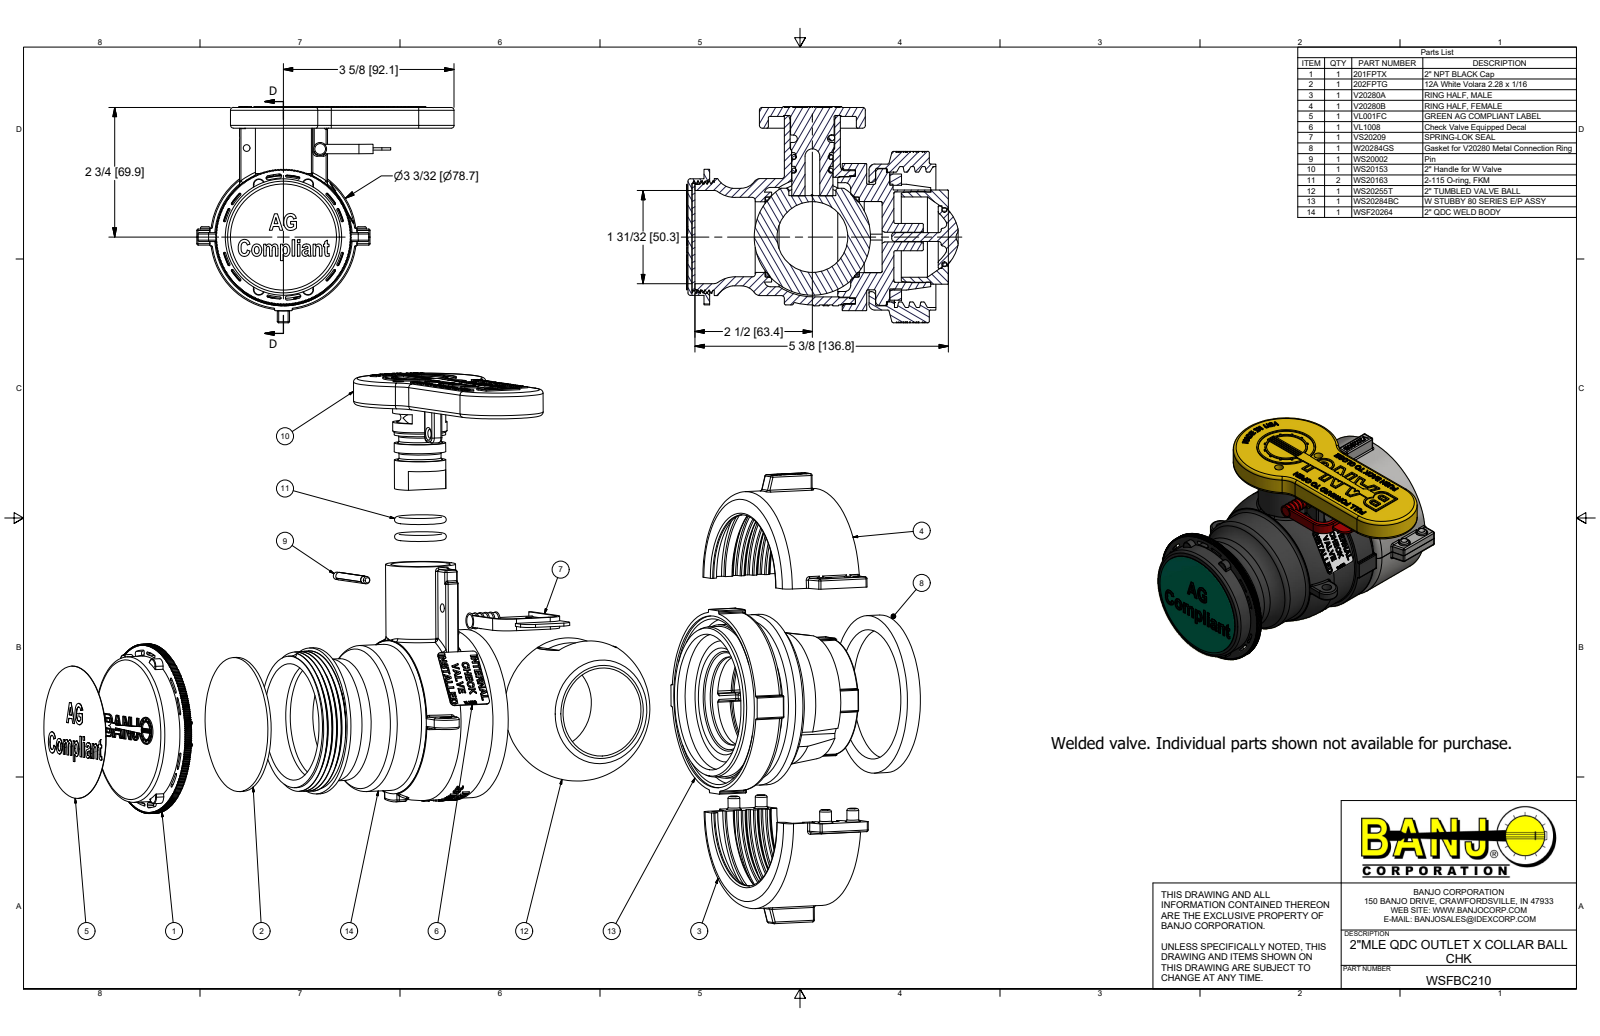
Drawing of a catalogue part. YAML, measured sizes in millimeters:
part_name: "WSF20264X; WS20258; WSF20264; WS20284R1BCX (+8 more)"
step_written_by: "Autodesk Inventor 2016 (AUTOMOTIVE_DESIGN)"
units: millimeters
bodies: {solids: 19, faces: 4465, planar: 2200, cylindrical: 1056, other: 1209}
overall_size: [146.3, 138.81, 116.66]
volume: 359269
surface_area: 187663
round_holes:
  - {diameter: 5.28, count: 4}
  - {diameter: 6.53, count: 4}
  - {diameter: 3.68, count: 2}
  - {diameter: 4.78, count: 2}
  - {diameter: 5.26, count: 2}
  - {diameter: 38.1, count: 2}
  - {diameter: 3.96, count: 1}
  - {diameter: 5.21, count: 1}
  - {diameter: 7.84, count: 1}
  - {diameter: 7.92, count: 1}
  - {diameter: 11.08, count: 1}
  - {diameter: 21.27, count: 1}
round_bosses_or_shafts:
  - {diameter: 5.08, count: 4}
  - {diameter: 57.15, count: 2}
  - {diameter: 30.23, count: 2}
  - {diameter: 78.74, count: 1}
  - {diameter: 77.42, count: 1}
  - {diameter: 74.17, count: 1}
  - {diameter: 73.66, count: 1}
  - {diameter: 73.15, count: 1}
partial_cylinders:
  - {radius: 0.76, count: 120}
  - {radius: 0.38, count: 32}
  - {radius: 0.4, count: 24}
  - {radius: 1.52, count: 4}
  - {radius: 1.59, count: 4}
  - {radius: 3, count: 4}
  - {radius: 6.35, count: 4}
  - {radius: 1.75, count: 3}
face_to_face_distances: [4.83, 1.6, 3.76, 2.16, 7.62, 105.13, 106.73, 108.89, 11.18, 97.51]
hole_center_spacings: [13.31, 39.68, 41.47, 51.95, 57.36, 63.87, 70.66, 74.38]
